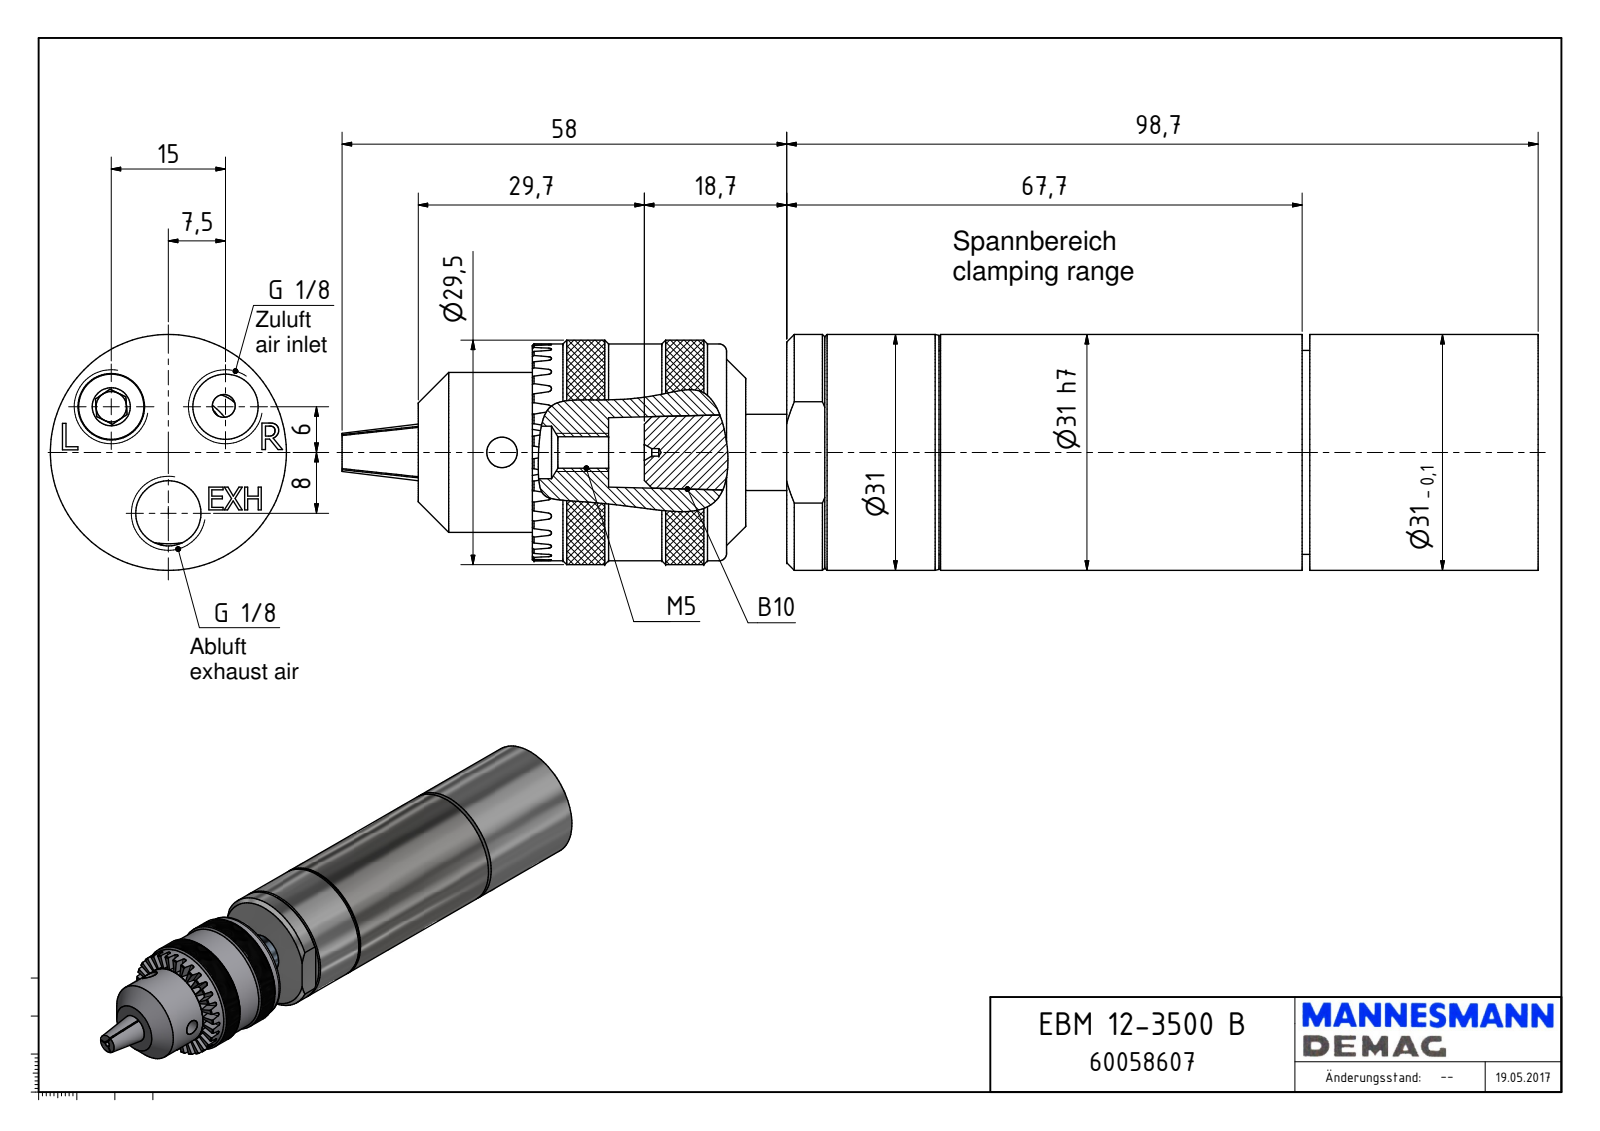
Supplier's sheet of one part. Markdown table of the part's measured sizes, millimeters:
| quantity | value |
| --- | --- |
| part name | EBM 12-3500 B_60058607 |
| STEP written by | Autodesk Inventor 2018 (CONFIG_CONTROL_DESIGN) |
| units | millimeters |
| bodies | 1 solid, 346 faces (223 planar, 57 cylindrical, 66 other) |
| overall size | 157.1 × 31 × 31 |
| volume | 94 232 mm³ |
| surface area | 19 139 mm² |
| round holes (diameter × count) | 4 × 4, 8.57 × 3, 1 × 1, 1.5 × 1, 4.13 × 1, 6.9 × 1, 10.5 × 1, 29.3 × 1 |
| round bosses / shafts (diameter × count) | 31 × 1, 29.5 × 1, 28.5 × 1, 26.79 × 1, 21 × 1, 10 × 1 |
| partial cylindrical surfaces (radius × count) | 0.5 × 23 |
| main face-to-face distances | 98.7, 5.4, 104.1, 25.6, 20.2, 78.5, 73.1, 67.7, 47.5, 31 |
| hole center spacings | 9.6, 15.88, 8, 15 |
